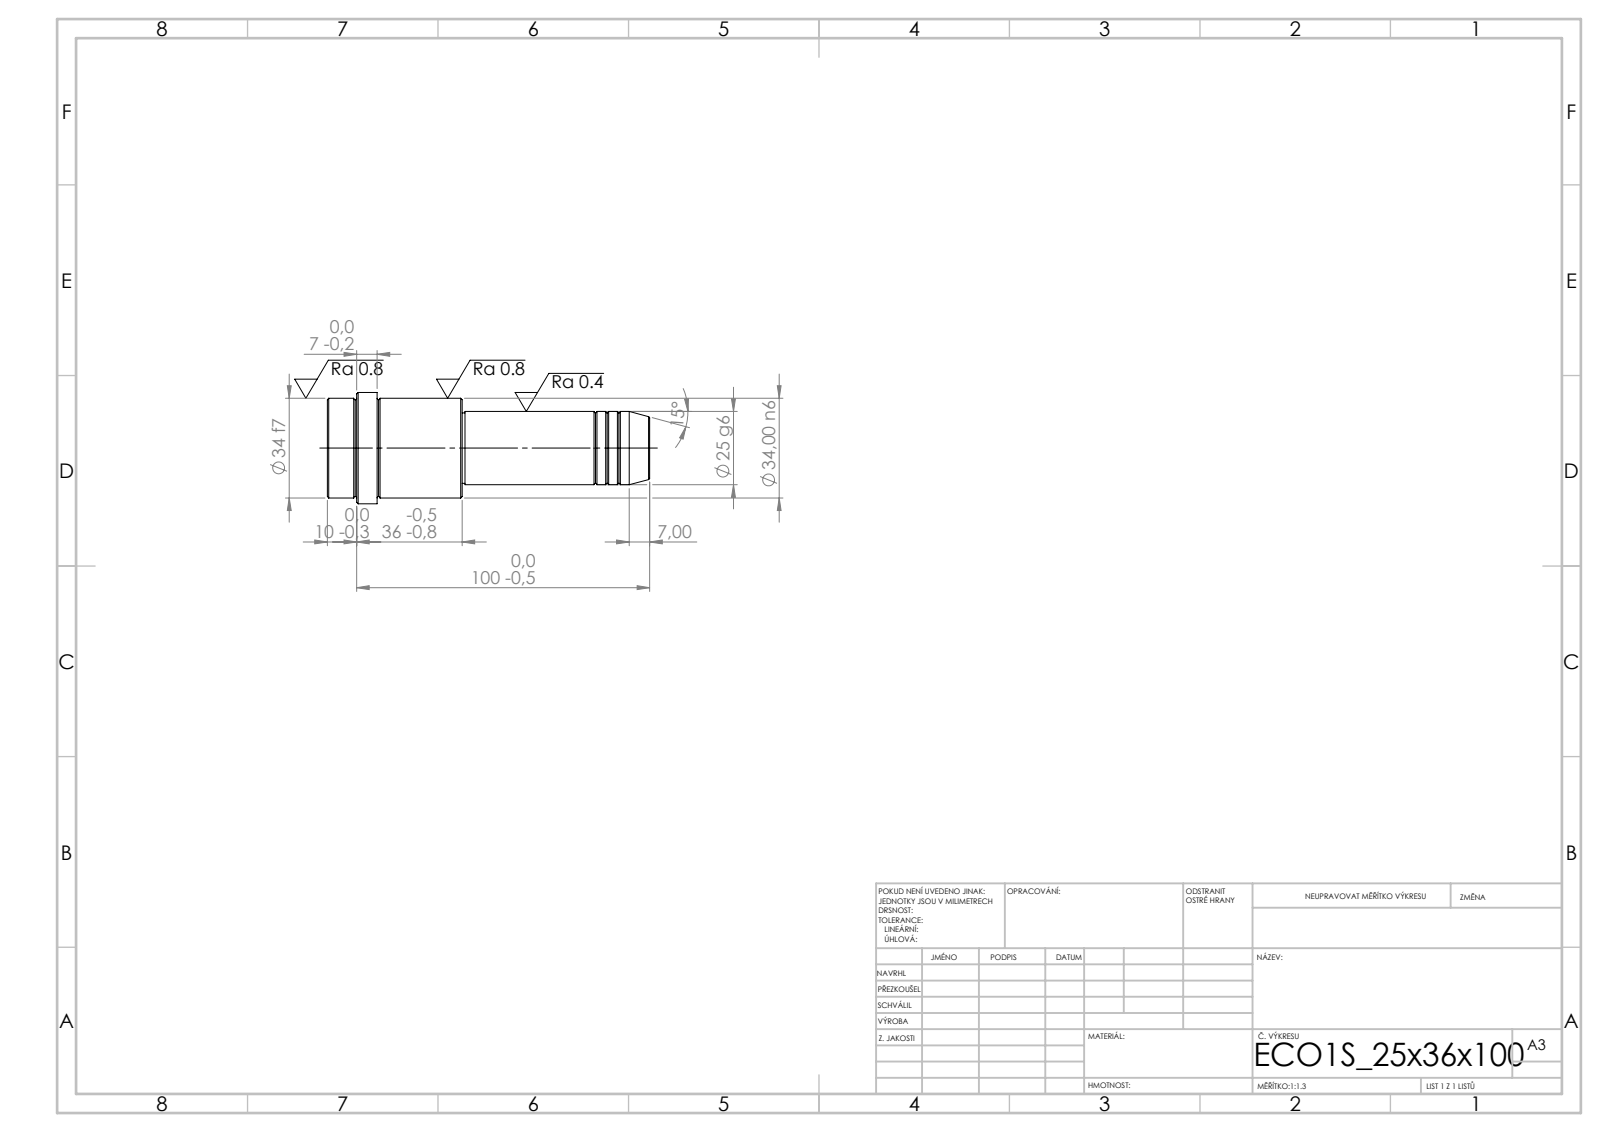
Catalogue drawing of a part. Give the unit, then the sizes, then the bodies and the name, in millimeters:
Units: millimetres
Overall size (bounding box): 110 × 38 × 38
Round bosses / shafts (diameter × count): ⌀38 ×1, ⌀34 ×1, ⌀25 ×1, ⌀24 ×1
Main face-to-face distances: 46, 64, 110, 93, 29, 17, 100, 36, 7, 10
Volume: 74 018 mm³ · Surface area: 12 345 mm²
Bodies: 1 solid, 52 faces (6 planar, 16 cylindrical, 30 other)
STEP written by: SolidWorks 2019 (CONFIG_CONTROL_DESIGN)
